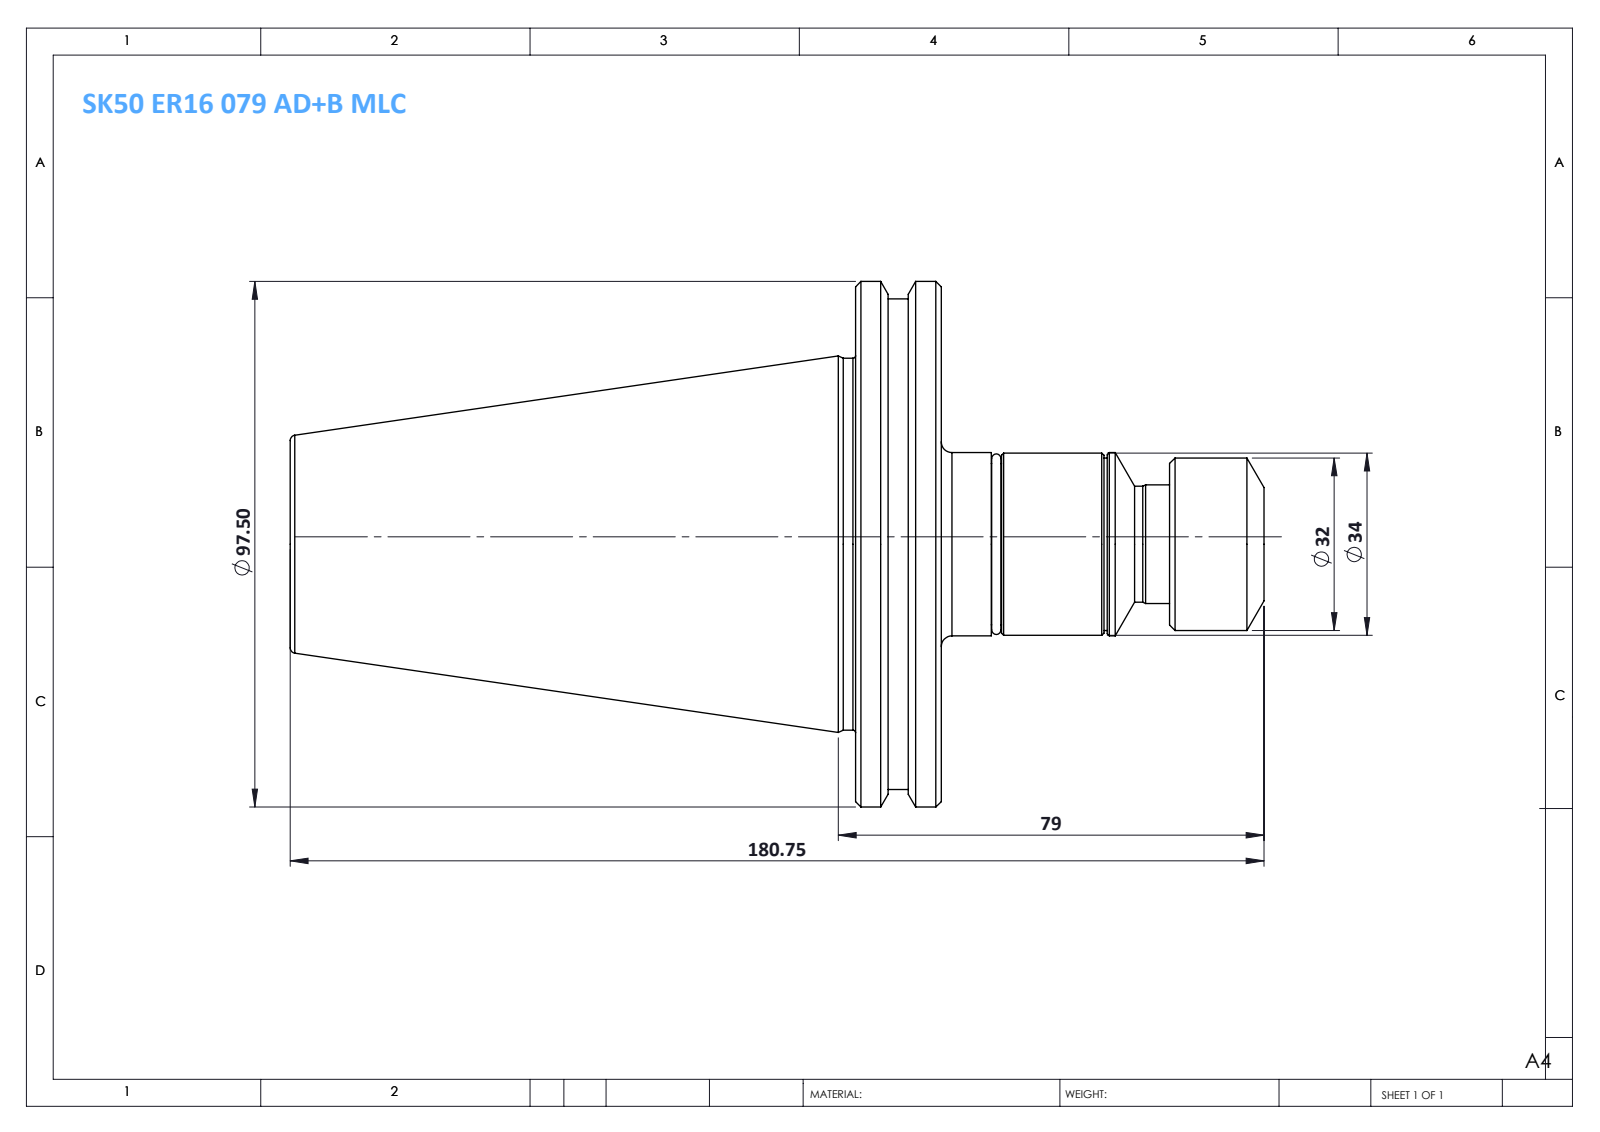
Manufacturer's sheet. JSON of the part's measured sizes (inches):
{"part_name": "SK 50 ER 16 079 AD+B MLC", "step_written_by": "SolidWorks 2014 (CONFIG_CONTROL_DESIGN)", "units": "inches", "bodies": {"solids": 2, "faces": 71, "planar": 11, "cylindrical": 24, "other": 36}, "overall_size": [7.116, 3.839, 3.839], "volume_in3": 25.66, "surface_area_in2": 67.95, "round_bosses_or_shafts": [[3.839, 1], [3.583, 1], [2.717, 1], [1.339, 1], [1.331, 1], [1.26, 1], [1.177, 1], [0.866, 1]], "face_to_face_distances": [0.626, 4.758, 4.132, 2.358, 2.984, 7.116, 0.689, 1.669, 2.295, 6.427]}
